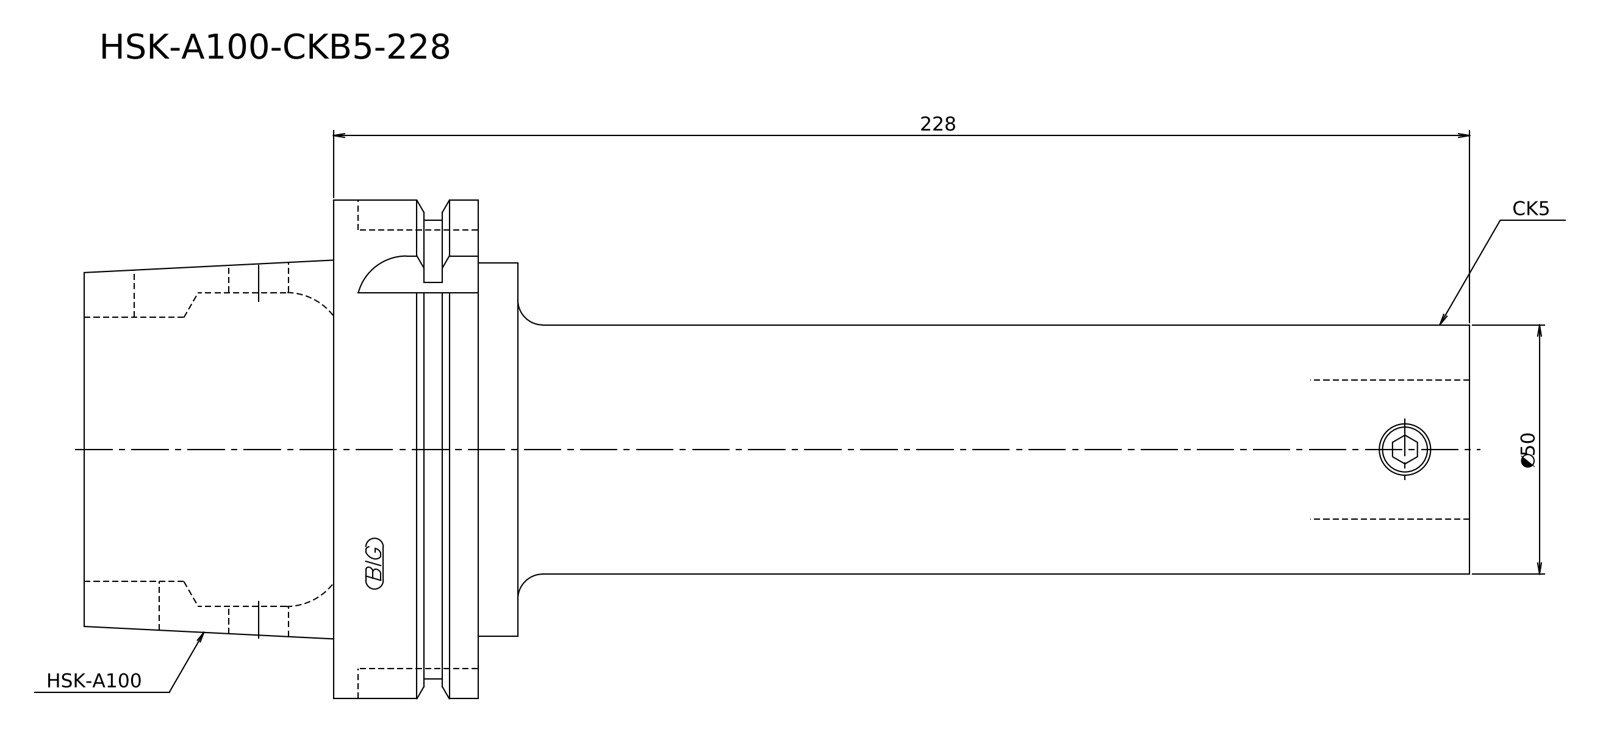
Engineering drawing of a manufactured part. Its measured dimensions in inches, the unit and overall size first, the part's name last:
Units: inches
Overall size (bounding box): 10.945 × 3.937 × 3.937
Round bosses / shafts (diameter × count): ⌀3.937 ×1, ⌀3.622 ×1, ⌀2.984 ×1, ⌀2.953 ×1, ⌀1.969 ×1
Main face-to-face distances: 3.11, 1.142, 1.969, 7.835, 8.976, 10.945, 7.52, 0.315, 1.457, 3.425
Volume: 51.68 in³ · Surface area: 106.9 in²
Bodies: 1 solid, 17 faces (7 planar, 6 cylindrical, 4 other)
STEP written by: Kubotek KeyCreator V8.5.1 (14335) (CONFIG_CONTROL_DESIGN)
